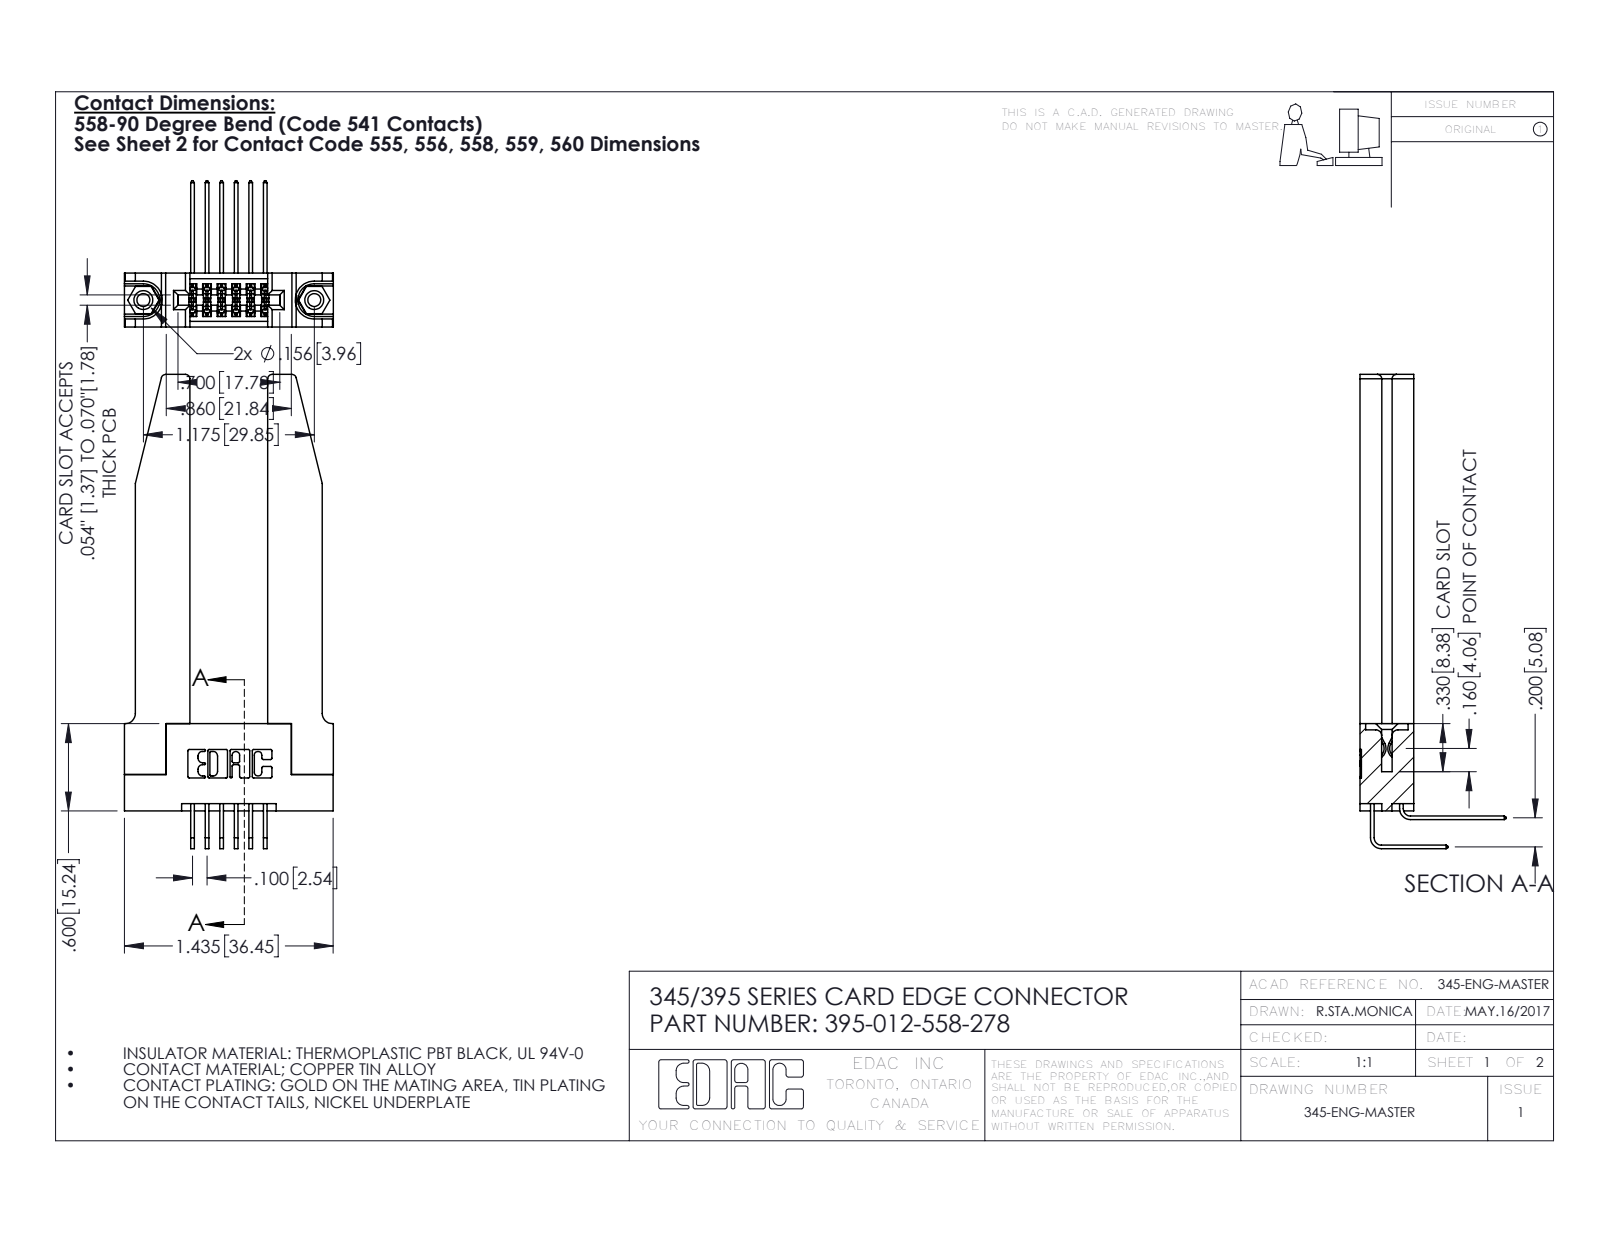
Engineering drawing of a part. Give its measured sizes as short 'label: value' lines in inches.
name: 345-292-001_558 559 Tail - 1; 345-292-001_558 Tail - 2; 345 Part_Flush Mounting Lugs - 0.156 Dia-TH; 345-220-078_345-220-078 (+2 more)
written by: SolidWorks 2016 (CONFIG_CONTROL_DESIGN)
unit: in
bodies: 17 solids, 984 faces (642 planar, 290 cylindrical, 52 other)
size: 3.259 × 1.436 × 1.005
volume: 0.674 in³; area: 17.53 in²
holes: 2× ⌀0.089, 2× ⌀0.125, 2× ⌀0.156, 1× ⌀0.064
bosses: 2× ⌀0.155
rounds: 22× R0.01, 19× R0.006, 8× R0.03, 6× R0.007, 6× R0.031, 3× R0.026, 2× R0.014, 2× R0.019
face distances: 0.37, 0.15, 0.22, 0.2, 0.072, 0.148, 0.535, 0.077, 0.298, 0.095
hole spacings: 0.27, 0.946, 1.175
